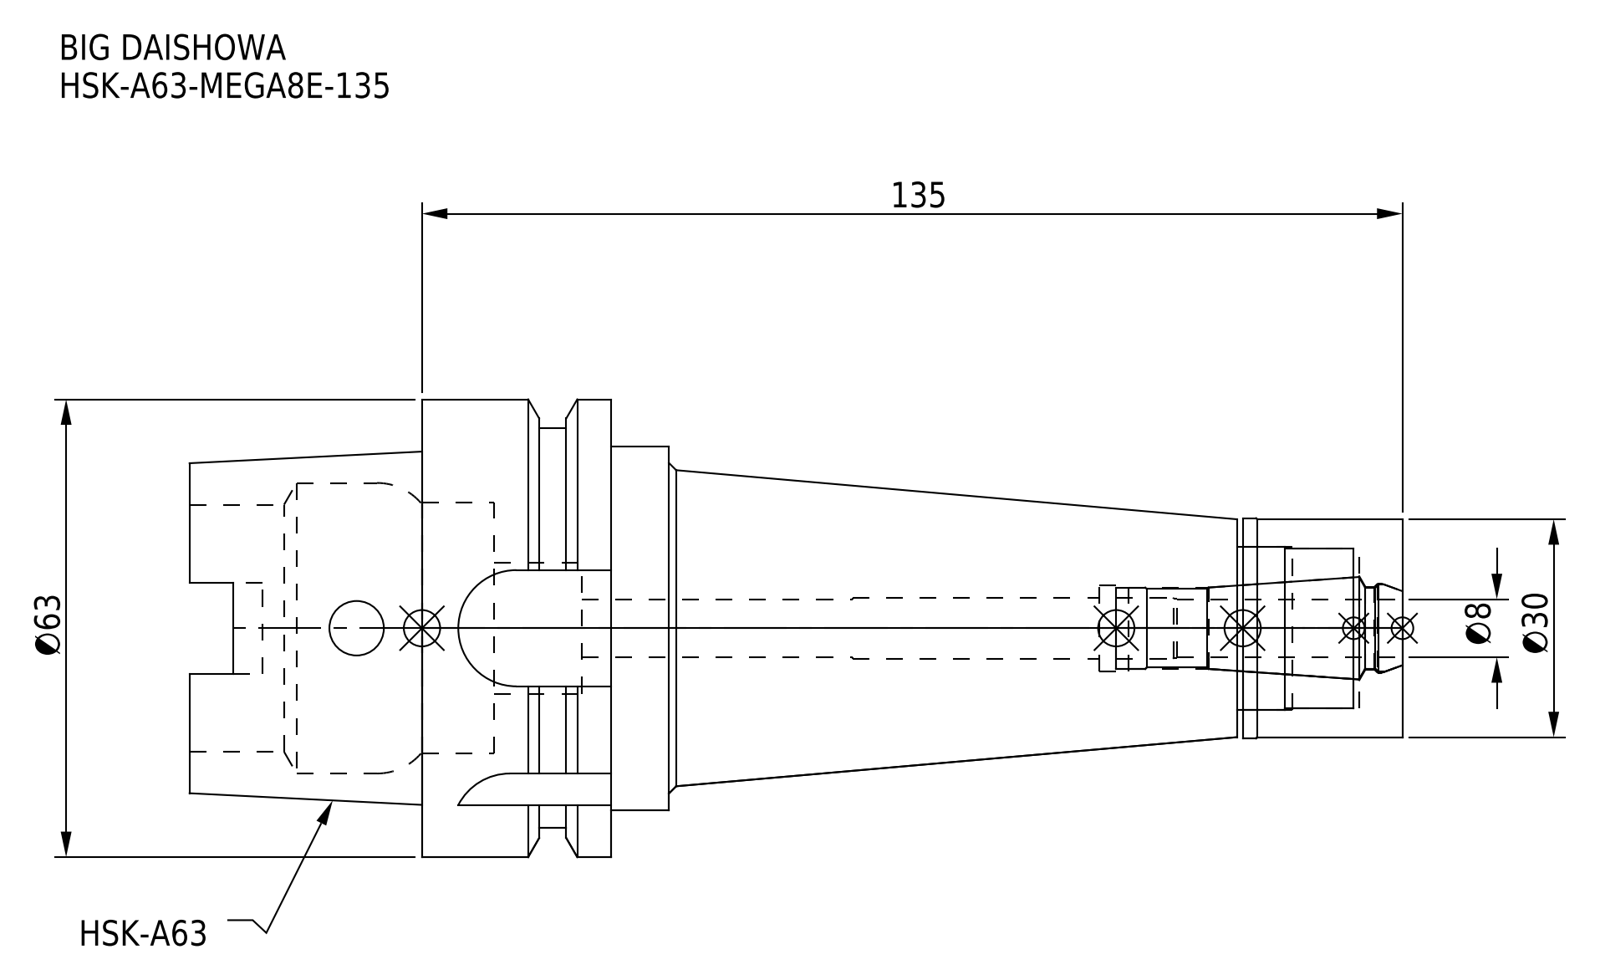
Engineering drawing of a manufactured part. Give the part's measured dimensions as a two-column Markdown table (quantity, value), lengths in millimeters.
| quantity | value |
| --- | --- |
| part name | DXF_TEMP_ASSY_ASM_4_ASM.stp; HSK-A63-MEGA8E-135-080.stp; MEN8_1.stp; HA63ME08135-080_ASM.stp (+3 more) |
| STEP written by | SolidWorks 2019 (CONFIG_CONTROL_DESIGN) |
| units | millimeters |
| bodies | 2 solids, 127 faces (45 planar, 54 cylindrical, 28 other) |
| overall size | 167 × 63 × 63 |
| volume | 189 156 mm³ |
| surface area | 40 605 mm² |
| round holes (diameter × count) | 7.5 × 1, 8 × 1, 8.4 × 1, 11.2 × 1, 11.4 × 1, 11.8 × 1, 12.3 × 1, 18 × 1, 22 × 1, 22.5 × 1, 34 × 1, 34.5 × 1 |
| round bosses / shafts (diameter × count) | 63 × 1, 55 × 1, 50 × 1, 30.3 × 1, 30 × 1 |
| partial cylindrical surfaces (radius × count) | 2.8 × 2, 2.88 × 2, 8 × 2, 9 × 1 |
| main face-to-face distances | 26, 135, 16.05, 9.95, 109, 125.05, 167, 58, 41.95, 32 |
